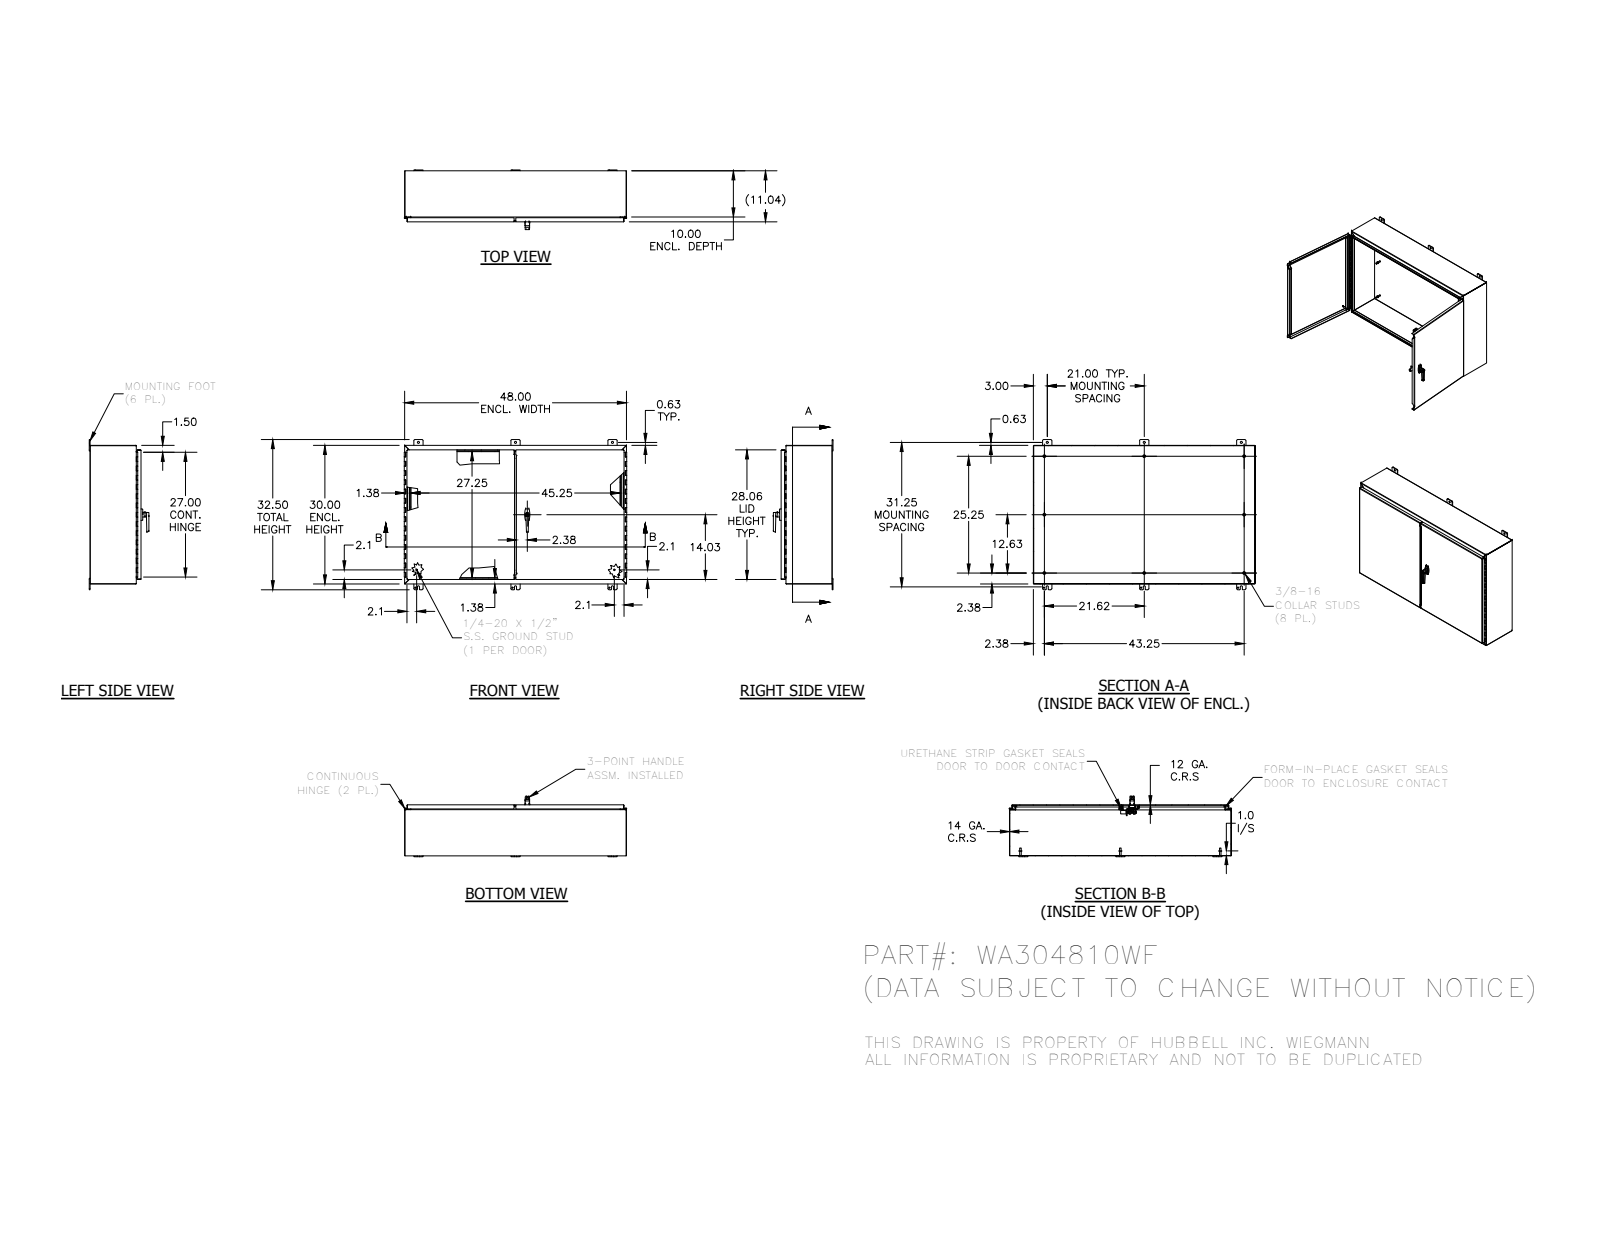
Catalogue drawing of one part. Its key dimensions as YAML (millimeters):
part_name: "WA304810WF; WA304810WFLRS; 34840; WA304810WFBTB (+8 more)"
step_written_by: "Autodesk Inventor 2012 (AUTOMOTIVE_DESIGN)"
units: millimeters
bodies: {solids: 60, faces: 2548, planar: 1400, cylindrical: 658, other: 490}
overall_size: [1223, 825.5, 328.1]
volume: 7407000
surface_area: 6849000
round_holes:
  - {diameter: 7, count: 8}
  - {diameter: 2.1, count: 6}
  - {diameter: 8, count: 6}
  - {diameter: 11.1, count: 6}
  - {diameter: 5.1, count: 4}
  - {diameter: 3.2, count: 2}
  - {diameter: 4, count: 2}
  - {diameter: 6.1, count: 2}
  - {diameter: 6.4, count: 2}
  - {diameter: 6.4, count: 2}
  - {diameter: 10.2, count: 2}
  - {diameter: 10.3, count: 2}
round_bosses_or_shafts:
  - {diameter: 4, count: 7}
  - {diameter: 15.9, count: 6}
  - {diameter: 8.4, count: 6}
  - {diameter: 6.4, count: 4}
  - {diameter: 2.9, count: 4}
  - {diameter: 25.4, count: 2}
  - {diameter: 14.3, count: 2}
  - {diameter: 13.4, count: 2}
partial_cylinders:
  - {radius: 0.8, count: 28}
  - {radius: 6.4, count: 24}
  - {radius: 0.2, count: 22}
  - {radius: 0.4, count: 22}
  - {radius: 2.7, count: 17}
  - {radius: 0.3, count: 16}
  - {radius: 1.3, count: 14}
  - {radius: 3.2, count: 12}
face_to_face_distances: [1.9, 2.4, 277.9, 276, 280.3, 278.4, 760.1, 1217.3, 758.2, 762]
hole_center_spacings: [533.4, 930.1, 7.4, 40.5, 762, 5.1, 517.2, 552.1]
